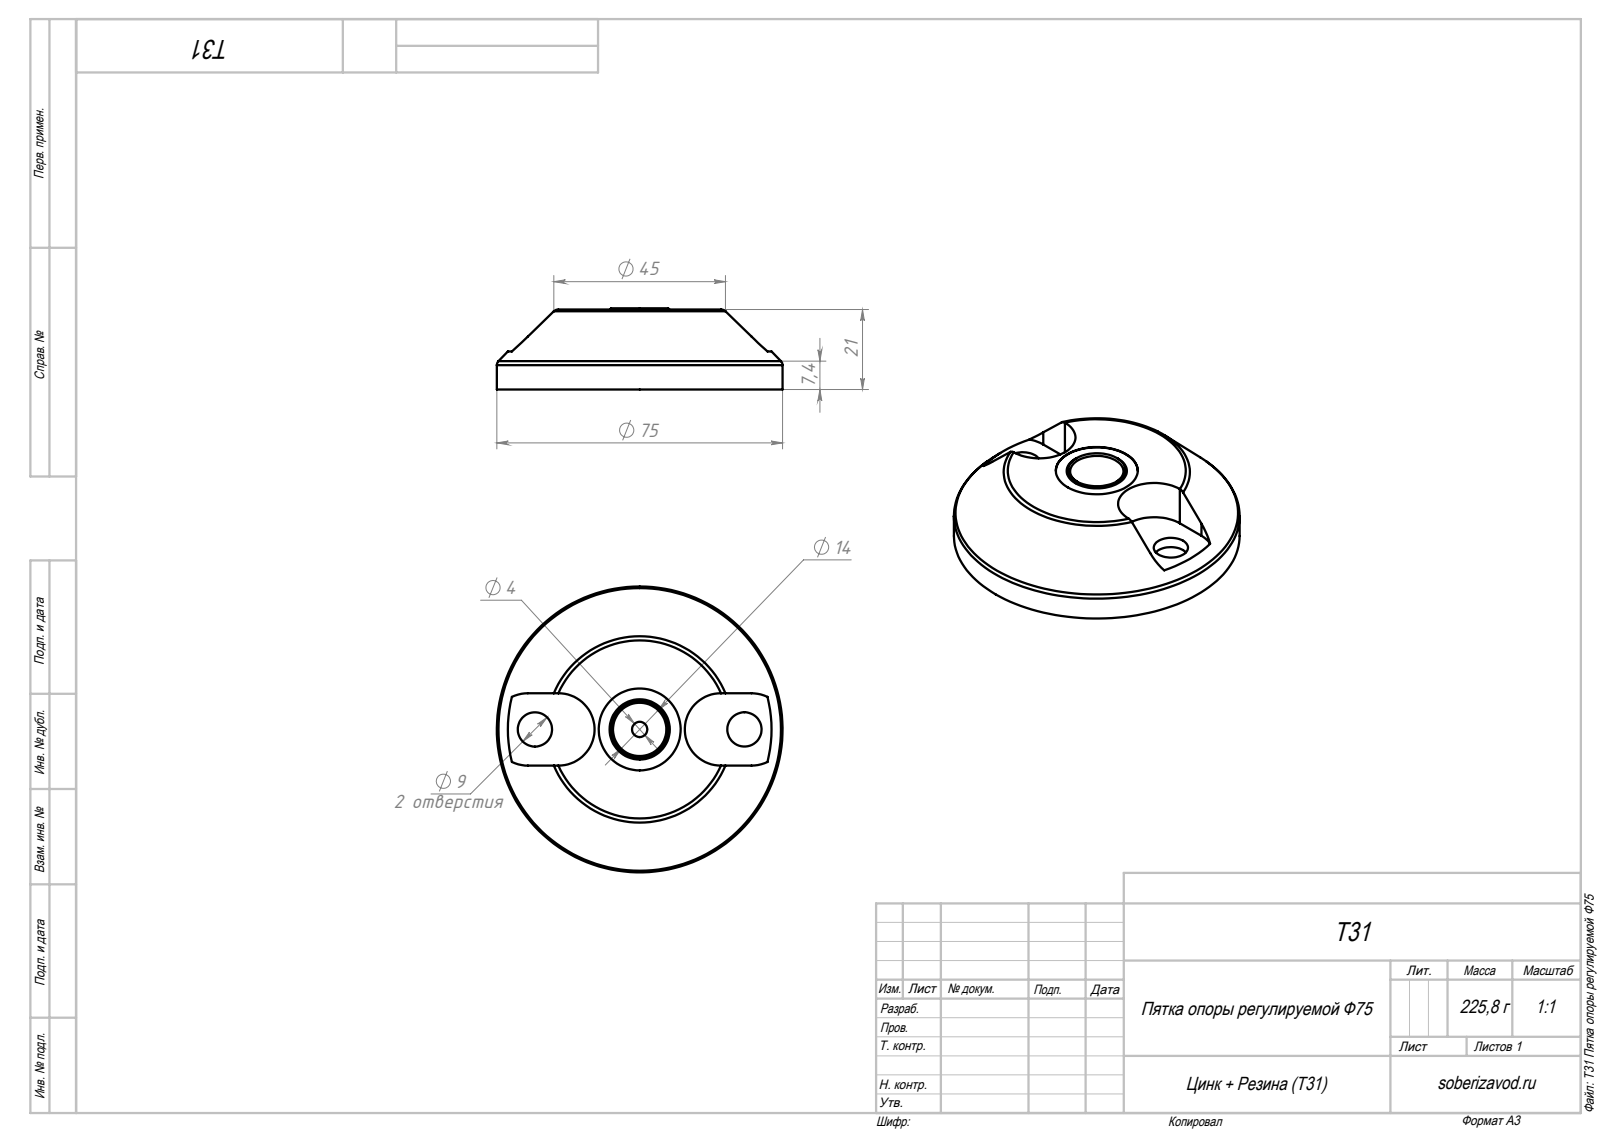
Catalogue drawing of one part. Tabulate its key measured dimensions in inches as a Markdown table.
| quantity | value |
| --- | --- |
| part name | T31 Пятка опоры регулируемой Ф75 |
| STEP written by | SolidWorks 2018 (AUTOMOTIVE_DESIGN) |
| units | inches |
| bodies | 1 solid, 46 faces (11 planar, 22 cylindrical, 13 other) |
| overall size | 2.953 × 2.953 × 0.839 |
| volume | 3.83 in³ |
| surface area | 20.83 in² |
| round holes (diameter × count) | 0.354 × 2, 0.433 × 2, 0.157 × 1, 0.551 × 1, 0.846 × 1 |
| round bosses / shafts (diameter × count) | 2.953 × 1 |
| partial cylindrical surfaces (radius × count) | 0.374 × 4 |
| main face-to-face distances | 0.827, 0.394, 0.433, 0.823, 0.429, 0.748, 0.276, 0.118, 0.547, 0.551 |
| hole center spacings | 1.083, 2.165 |
